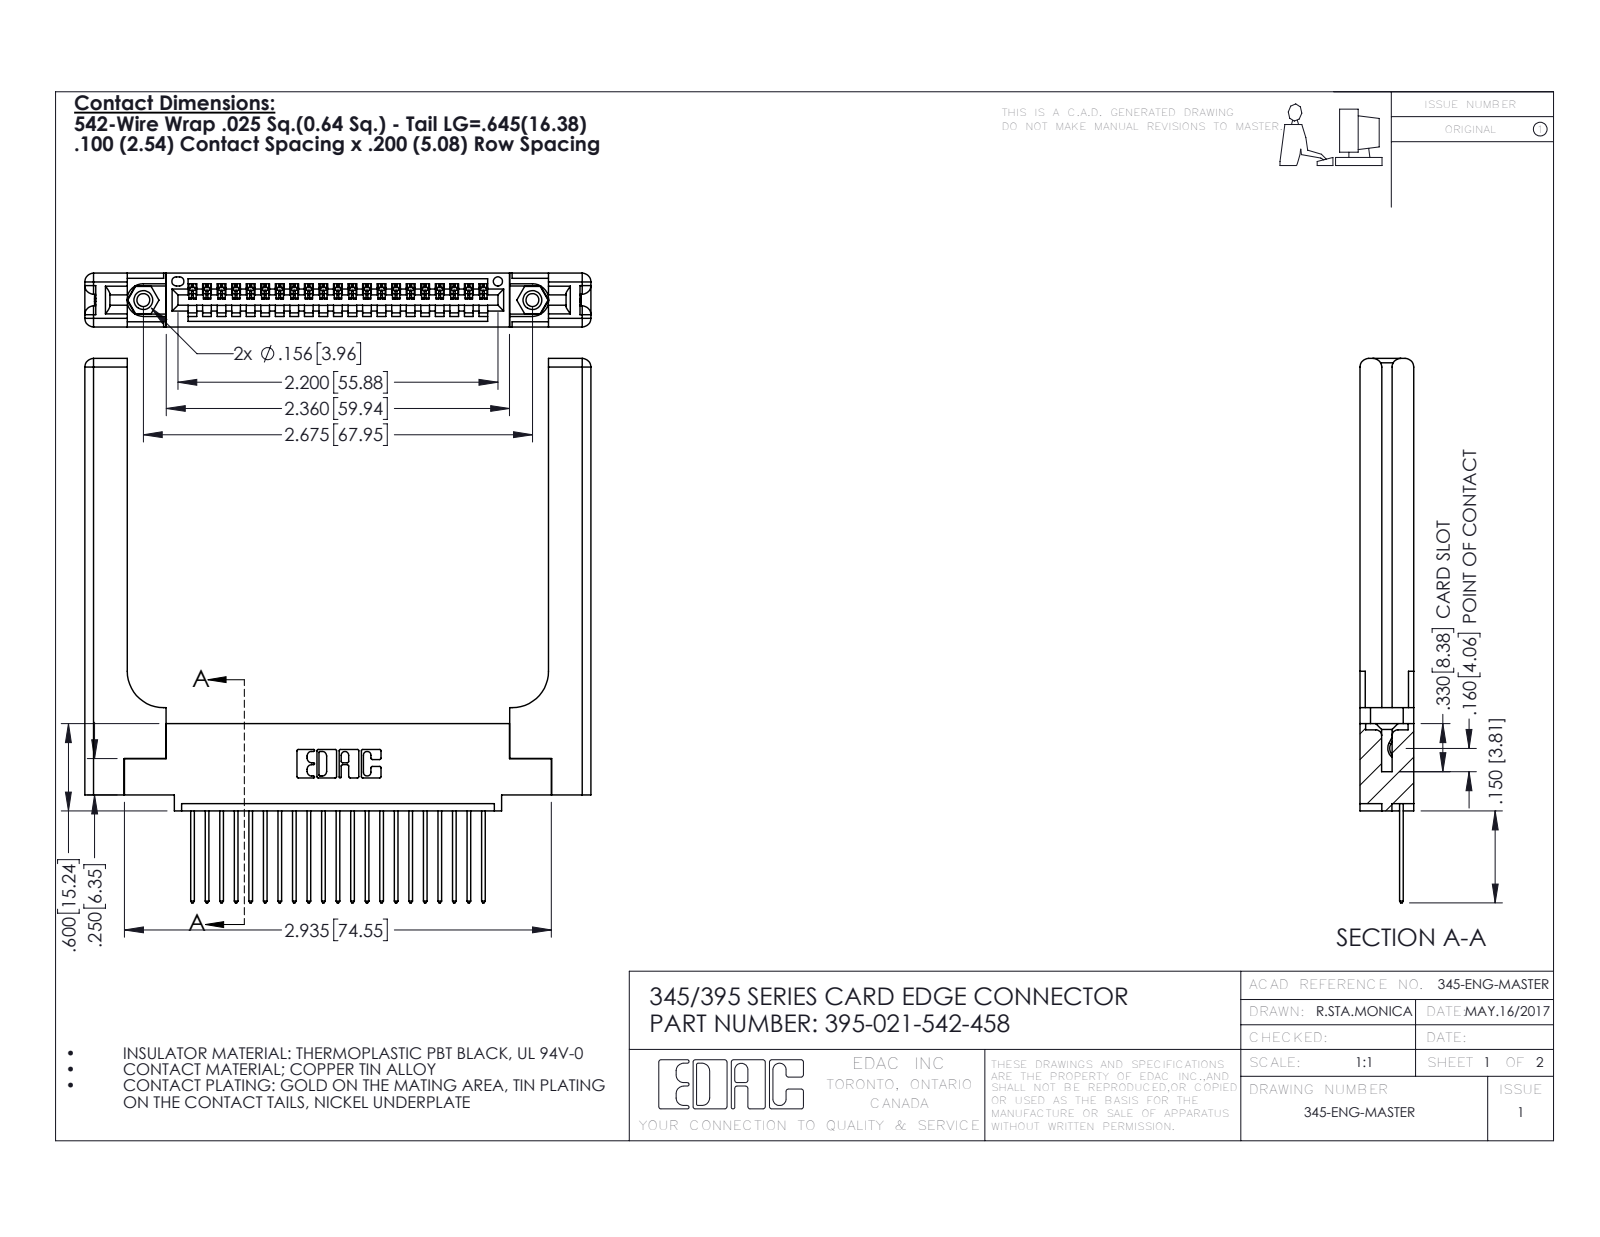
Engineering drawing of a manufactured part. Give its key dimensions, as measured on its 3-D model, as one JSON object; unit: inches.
{"part_name": "345-220-058_345-220-058; 345-292-001_345-293-142; 395-021-542-458; 345 Part_0.110 Offset - 0.156 Dia-TH (+1 more)", "step_written_by": "SolidWorks 2016 (CONFIG_CONTROL_DESIGN)", "units": "inches", "bodies": {"solids": 26, "faces": 1604, "planar": 1072, "cylindrical": 472, "other": 60}, "overall_size": [3.742, 3.479, 0.37], "volume_in3": 1.019, "surface_area_in2": 25.25, "round_holes": [[0.089, 2], [0.125, 2], [0.156, 2], [0.064, 1]], "round_bosses_or_shafts": [[0.155, 2]], "partial_cylinders_radius": [[0.006, 42], [0.01, 42], [0.01, 22], [0.06, 16], [0.007, 6], [0.031, 6], [0.026, 3], [0.03, 2]], "face_to_face_distances": [0.37, 0.072, 0.298, 0.148, 0.15, 0.077, 0.098, 0.272, 0.025, 0.22], "hole_center_spacings": [0.27, 2.441, 2.675]}
